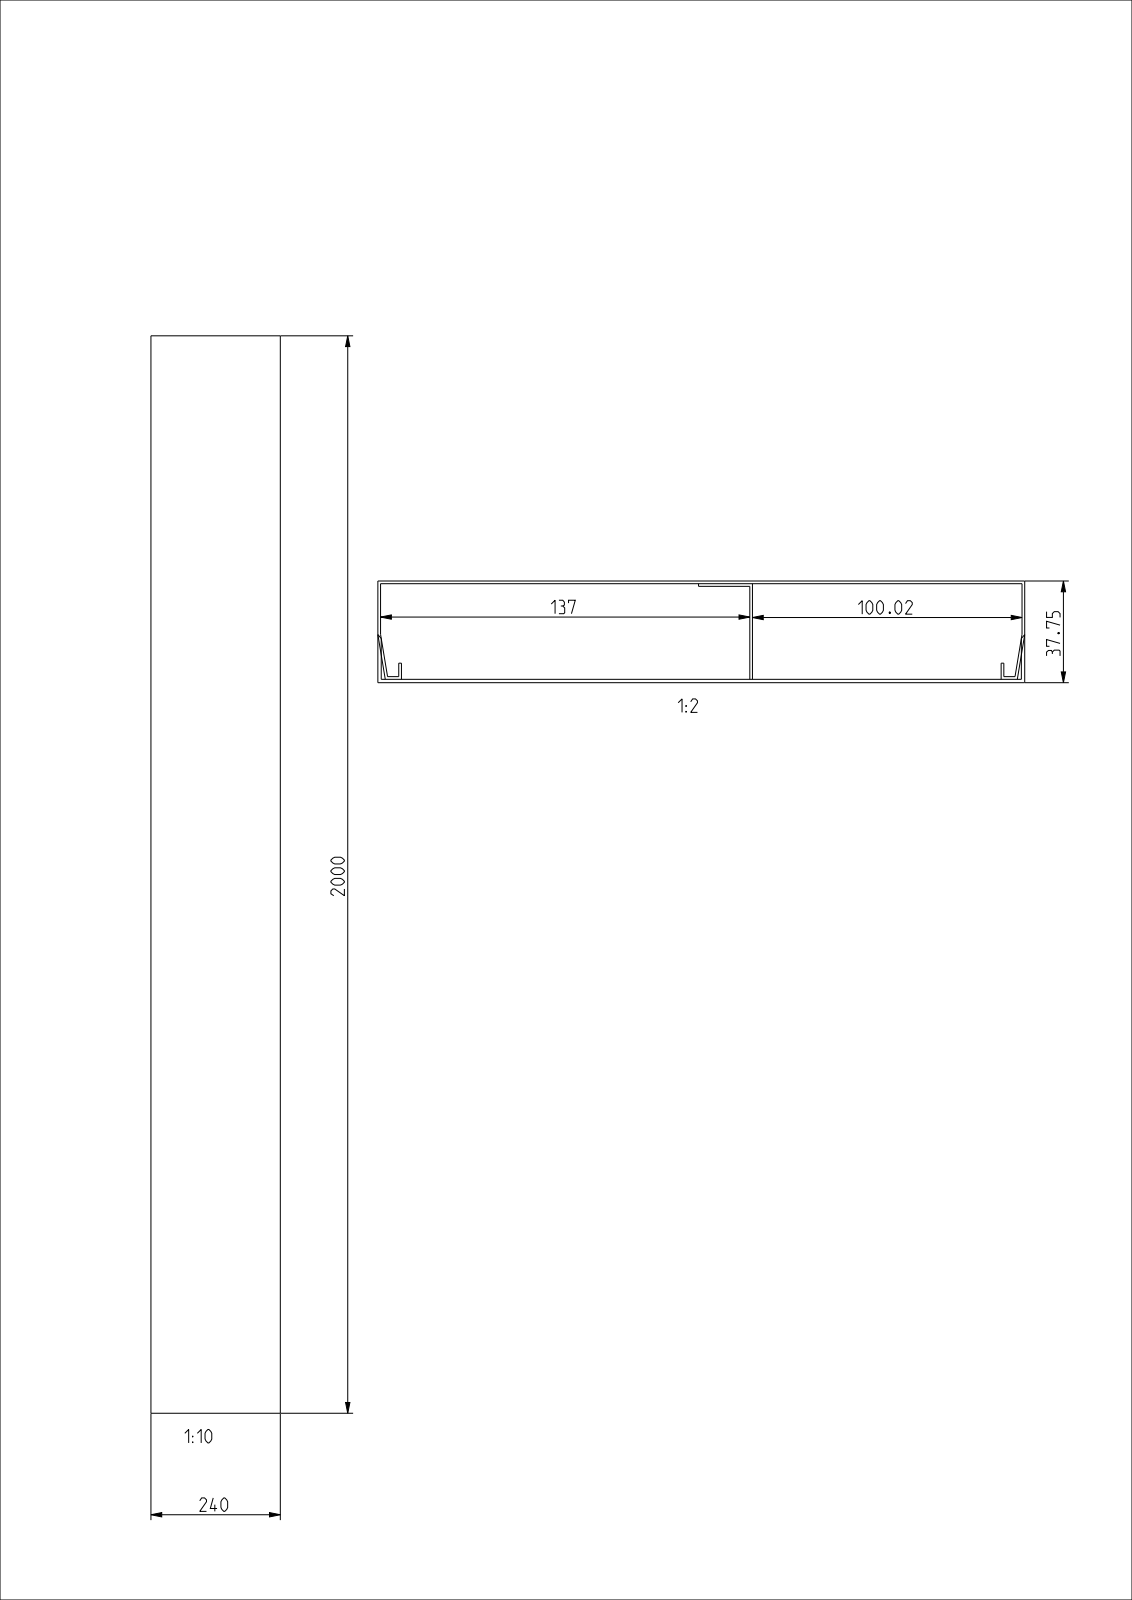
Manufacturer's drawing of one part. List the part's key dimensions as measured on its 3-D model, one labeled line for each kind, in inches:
Part name (STEP PRODUCT): UK240382KUN_OBERTEIL; UK240382KUN_UNTERTEIL; UK240382KUN_ASM
STEP written by: CREO PARAMETRIC BY PTC INC, 2022024 (AUTOMOTIVE_DESIGN)
Units: inches
Bodies: 2 solids, 39 faces (39 planar, 0 cylindrical, 0 other)
Overall size (bounding box): 78.74 × 9.449 × 1.486
Volume: 88.42 in³ · Surface area: 3 980 in²
Main face-to-face distances: 0.039, 0.049, 1.437, 1.486, 1.398, 1.447, 0.039, 9.449, 9.409, 5.472
